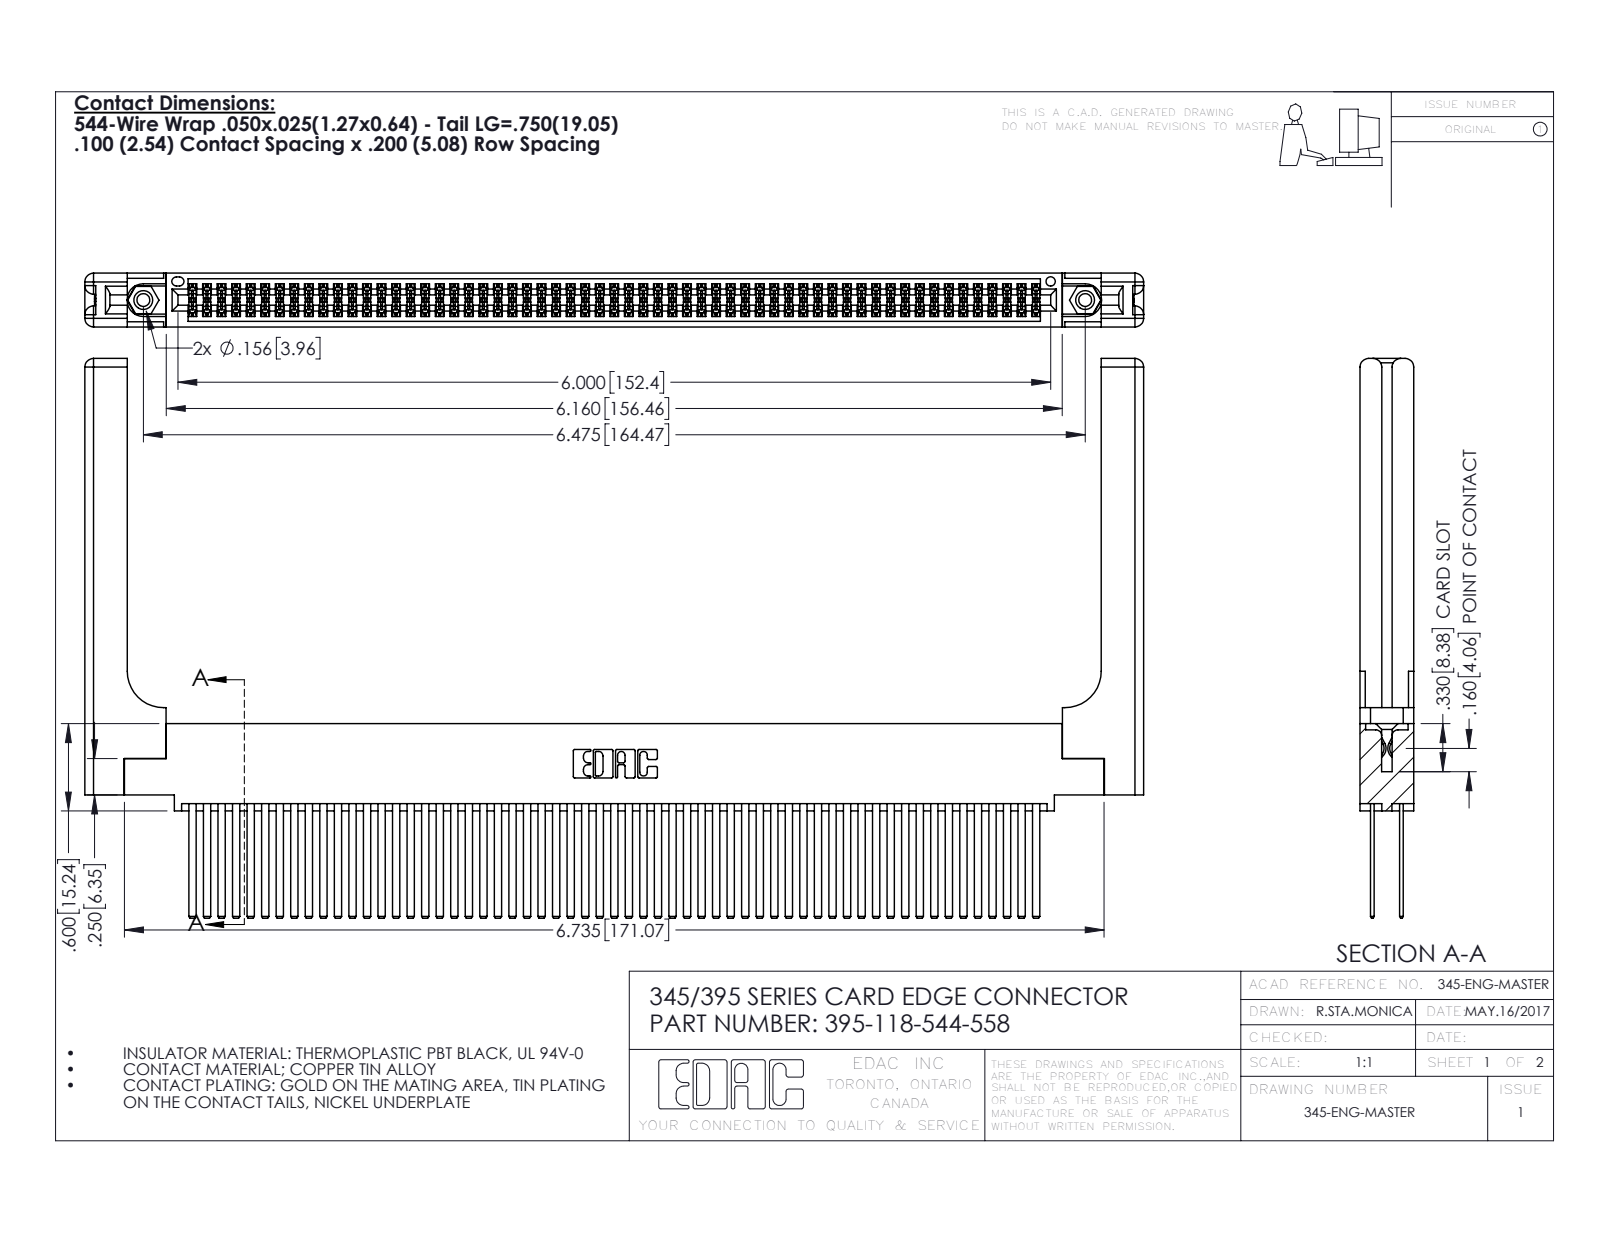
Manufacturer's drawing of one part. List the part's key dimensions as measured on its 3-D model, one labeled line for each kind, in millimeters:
Part name (STEP PRODUCT): 345-250-001_345-250-001-102; 345-292-001_345-293-144; 345 Part_0.110 Offset - 0.156 Dia-TH; 395-118-544-558 (+1 more)
STEP written by: SolidWorks 2016 (CONFIG_CONTROL_DESIGN)
Units: millimetres
Bodies: 123 solids, 5578 faces (3654 planar, 1864 cylindrical, 60 other)
Overall size (bounding box): 184.9 × 97.7 × 9.4
Volume: 28 170 mm³ · Surface area: 39 450 mm²
Round holes (diameter × count): ⌀2.3 ×2, ⌀3.2 ×2, ⌀4 ×2, ⌀1.6 ×1
Round bosses / shafts (diameter × count): ⌀3.9 ×2
Partial cylindrical surfaces — rounded edges, fillets, slot ends (radius × count): R0.2 ×177, R0.3 ×22, R1.5 ×16, R0.2 ×6, R0.8 ×6, R0.7 ×3, R0.4 ×2, R0.5 ×2
Main face-to-face distances: 1.8, 7.6, 2.5, 6.9, 0.6, 5.1, 5.7, 9.4, 4.4, 3.8
Hole centre spacings: 6.9, 158.5, 164.5
